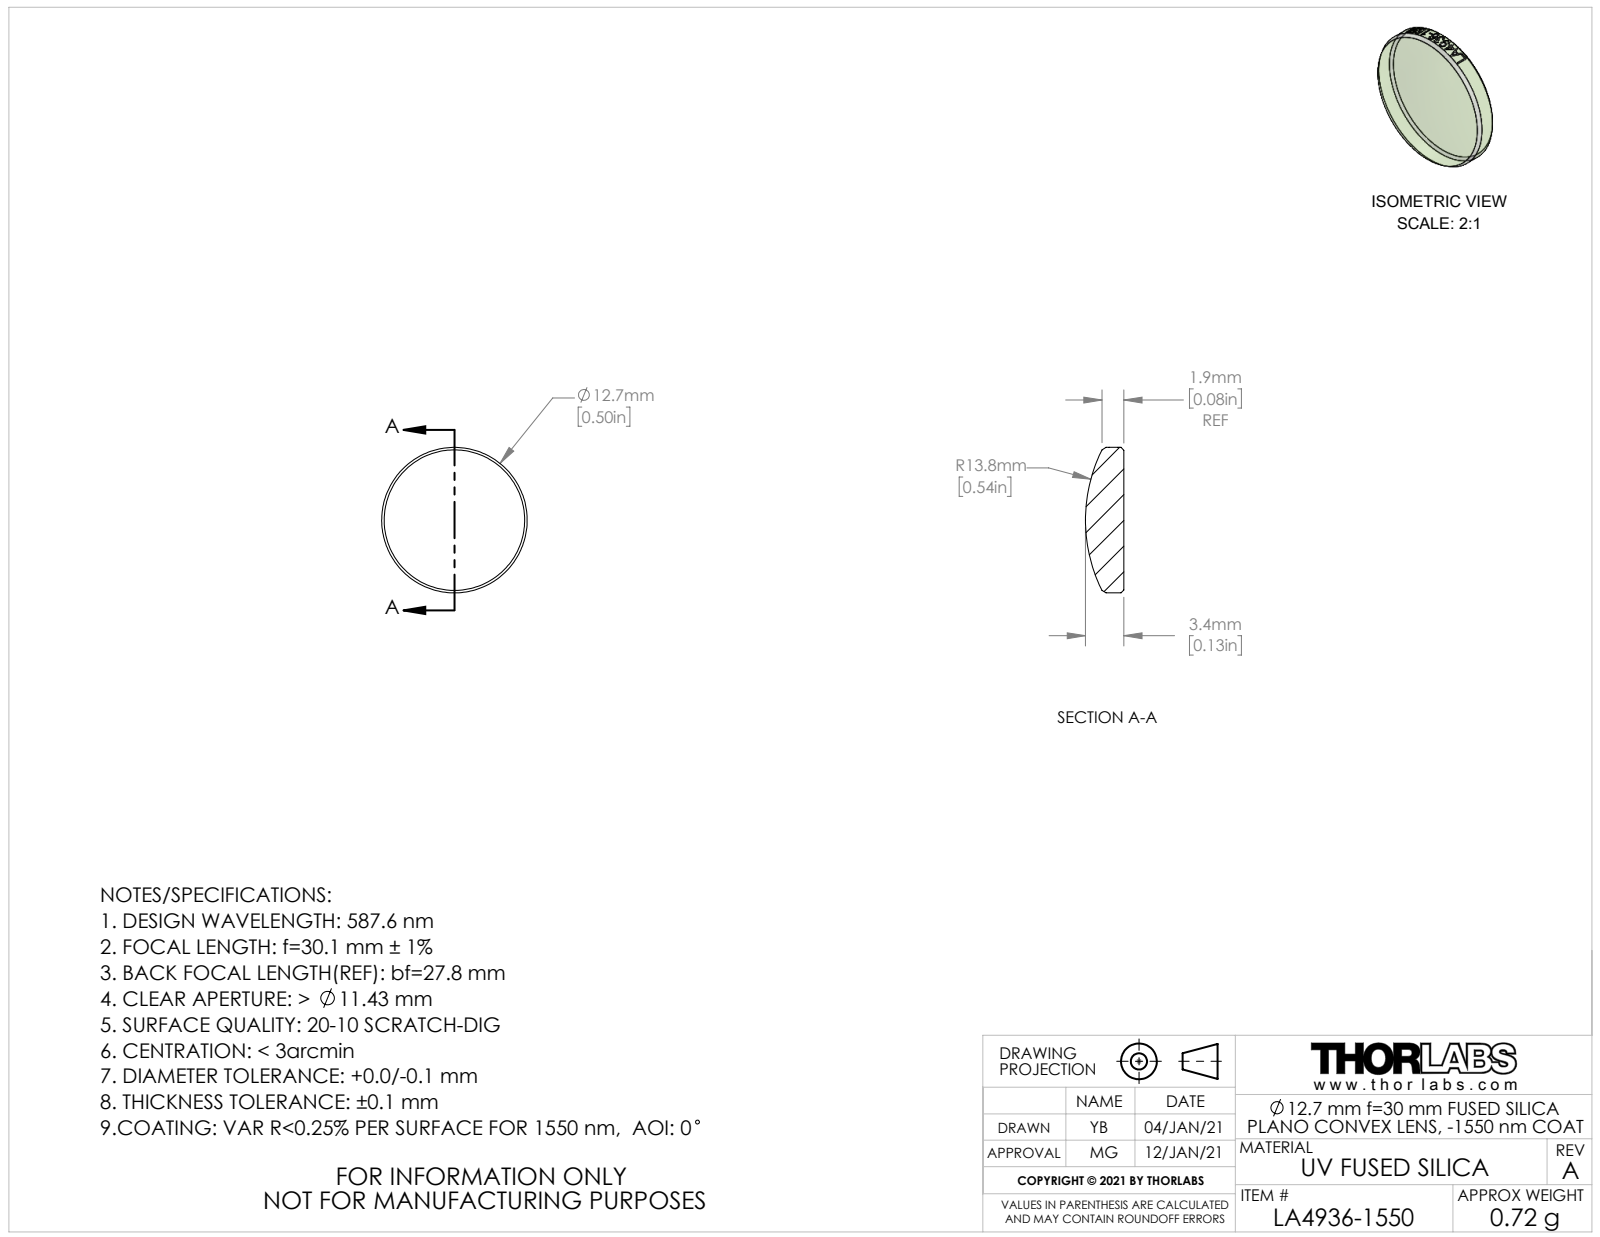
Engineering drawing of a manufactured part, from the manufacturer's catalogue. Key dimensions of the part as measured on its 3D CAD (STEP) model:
Part name (STEP PRODUCT): CTN015940-E0W
STEP written by: SolidWorks 2018 (AUTOMOTIVE_DESIGN)
Units: inches
Bodies: 1 solid, 25 faces (1 planar, 18 cylindrical, 6 other)
Overall size (bounding box): 0.5 × 0.5 × 0.131
Volume: 0.02 in³ · Surface area: 0.502 in²
Round bosses / shafts (diameter × count): ⌀0.5 ×1
